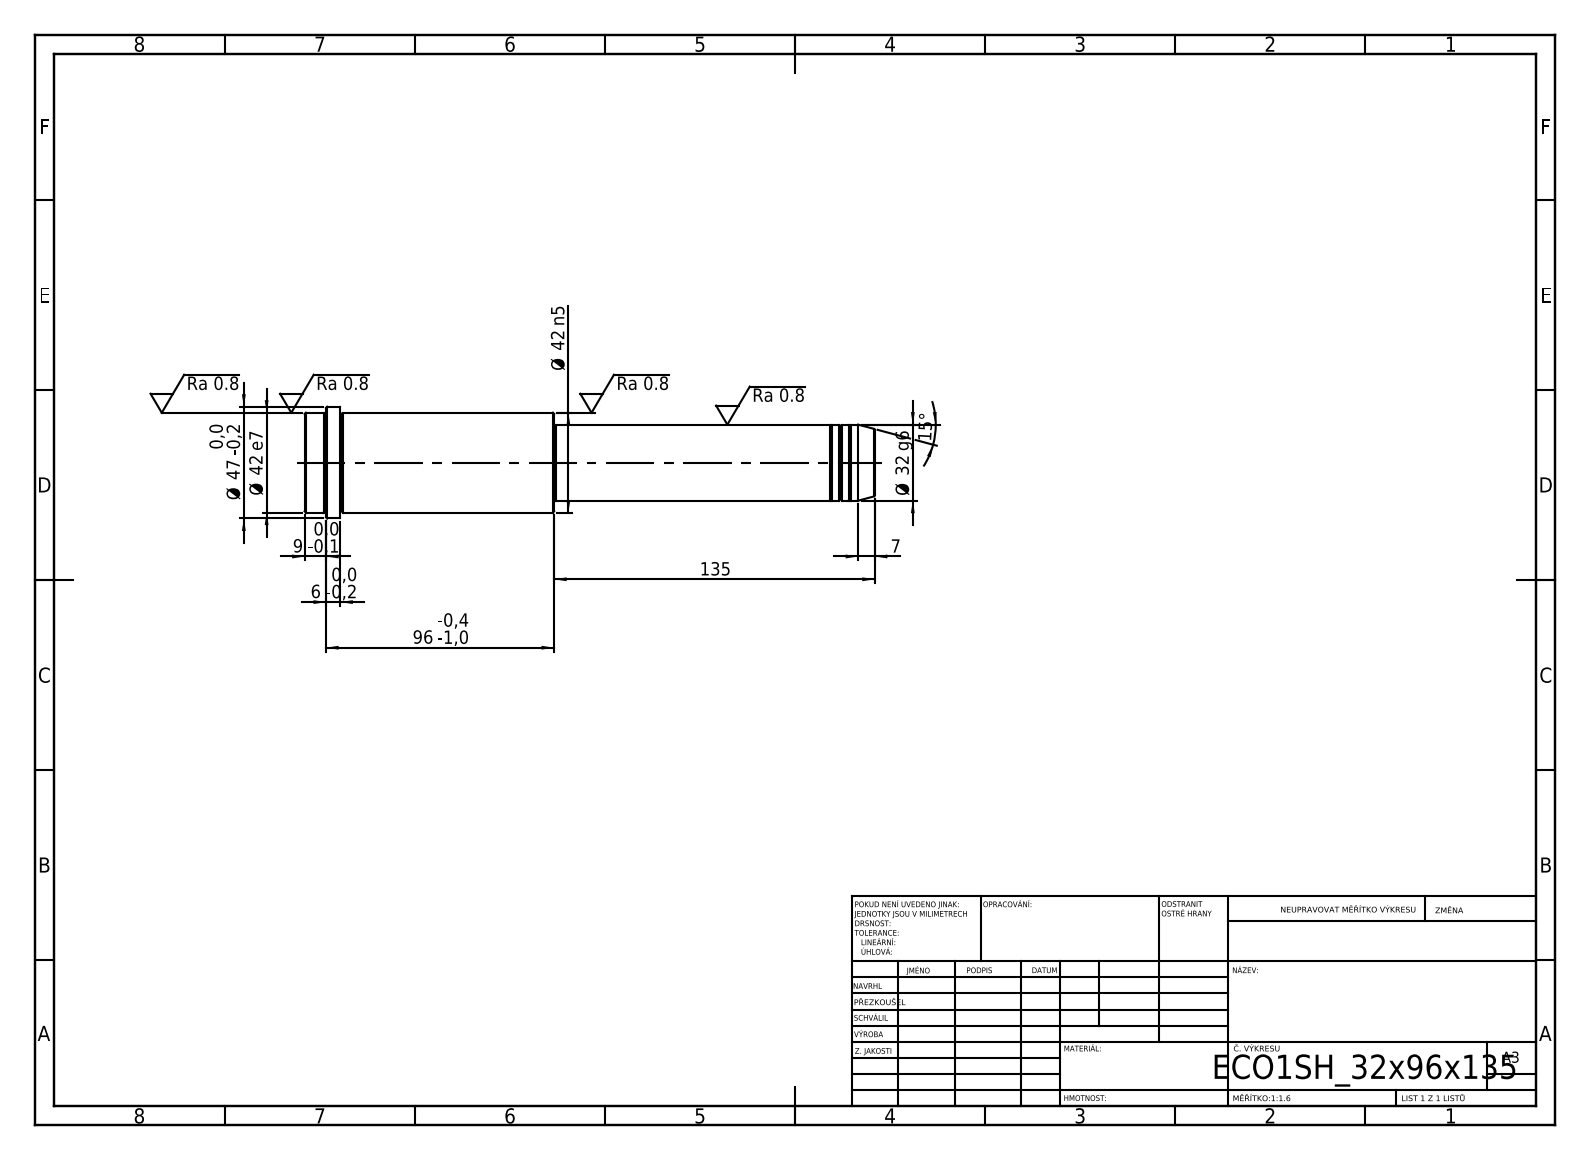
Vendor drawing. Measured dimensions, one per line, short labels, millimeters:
written by: SolidWorks 2019 (CONFIG_CONTROL_DESIGN)
unit: mm
bodies: 1 solid, 52 faces (6 planar, 16 cylindrical, 30 other)
size: 240 × 47 × 47
volume: 255 185 mm³; area: 31 066 mm²
bosses: 1× ⌀47, 1× ⌀42, 1× ⌀32, 1× ⌀31
face distances: 240, 135, 105, 225, 90, 15, 231, 96, 6, 9
